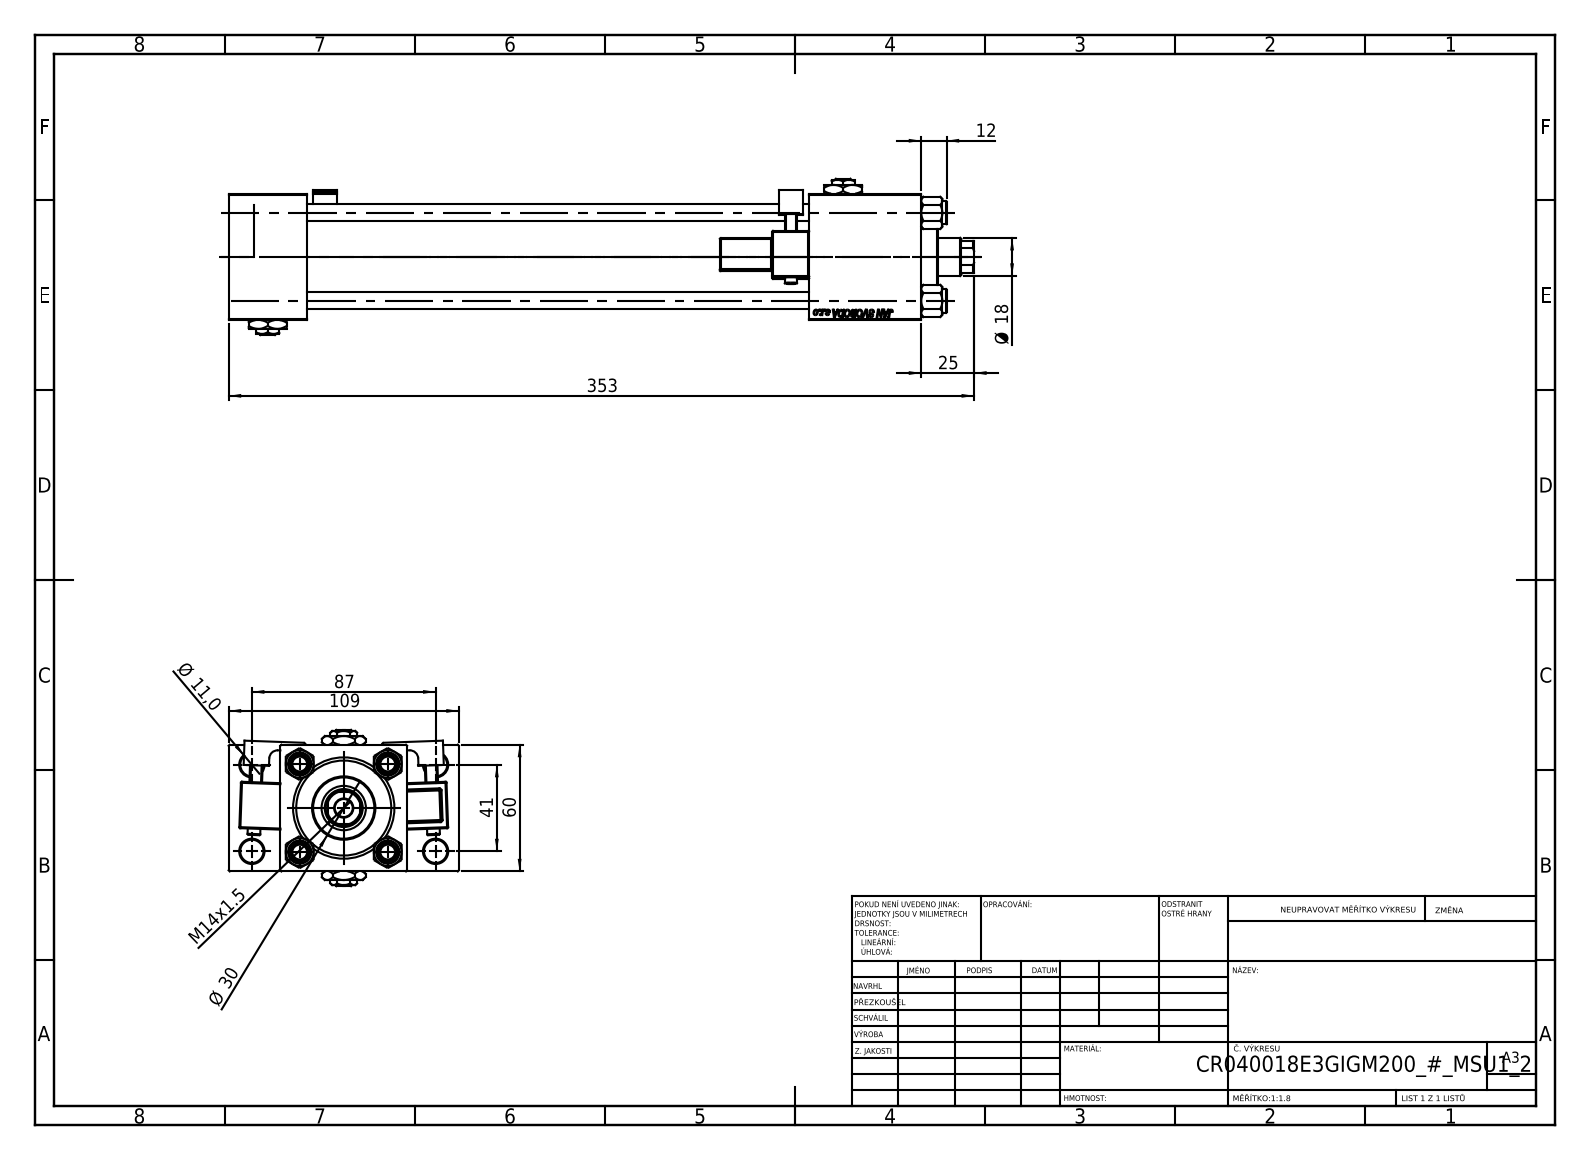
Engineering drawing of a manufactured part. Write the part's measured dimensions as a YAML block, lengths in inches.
part_name: "V215CR_E_Body; V215_VC_A; NUT_M5_E; V215CR_TYCINKA_E (+3 more)"
step_written_by: "SolidWorks 2019 (CONFIG_CONTROL_DESIGN)"
units: inches
bodies: {solids: 15, faces: 1385, planar: 602, cylindrical: 153, other: 630}
overall_size: [13.898, 4.291, 2.913]
volume: 42.43
surface_area: 334.8
round_holes:
  - {diameter: 0.315, count: 4}
  - {diameter: 0.433, count: 4}
  - {diameter: 0.276, count: 3}
  - {diameter: 0.656, count: 3}
  - {diameter: 0.945, count: 3}
  - {diameter: 0.335, count: 1}
  - {diameter: 0.709, count: 1}
  - {diameter: 0.827, count: 1}
  - {diameter: 1.22, count: 1}
  - {diameter: 1.575, count: 1}
  - {diameter: 1.772, count: 1}
round_bosses_or_shafts:
  - {diameter: 0.433, count: 4}
  - {diameter: 0.236, count: 2}
  - {diameter: 1.811, count: 1}
  - {diameter: 1.181, count: 1}
partial_cylinders:
  - {radius: 0.02, count: 48}
  - {radius: 0.039, count: 2}
  - {radius: 0.098, count: 2}
  - {radius: 0.157, count: 2}
  - {radius: 0.335, count: 1}
face_to_face_distances: [2.362, 1.457, 0.965, 3.327, 2.087, 12.913, 11.457, 10.827, 9.37, 0.957]
hole_center_spacings: [0.892, 1.161, 1.642, 1.856, 1.893, 2.533, 3.011, 1.614]
